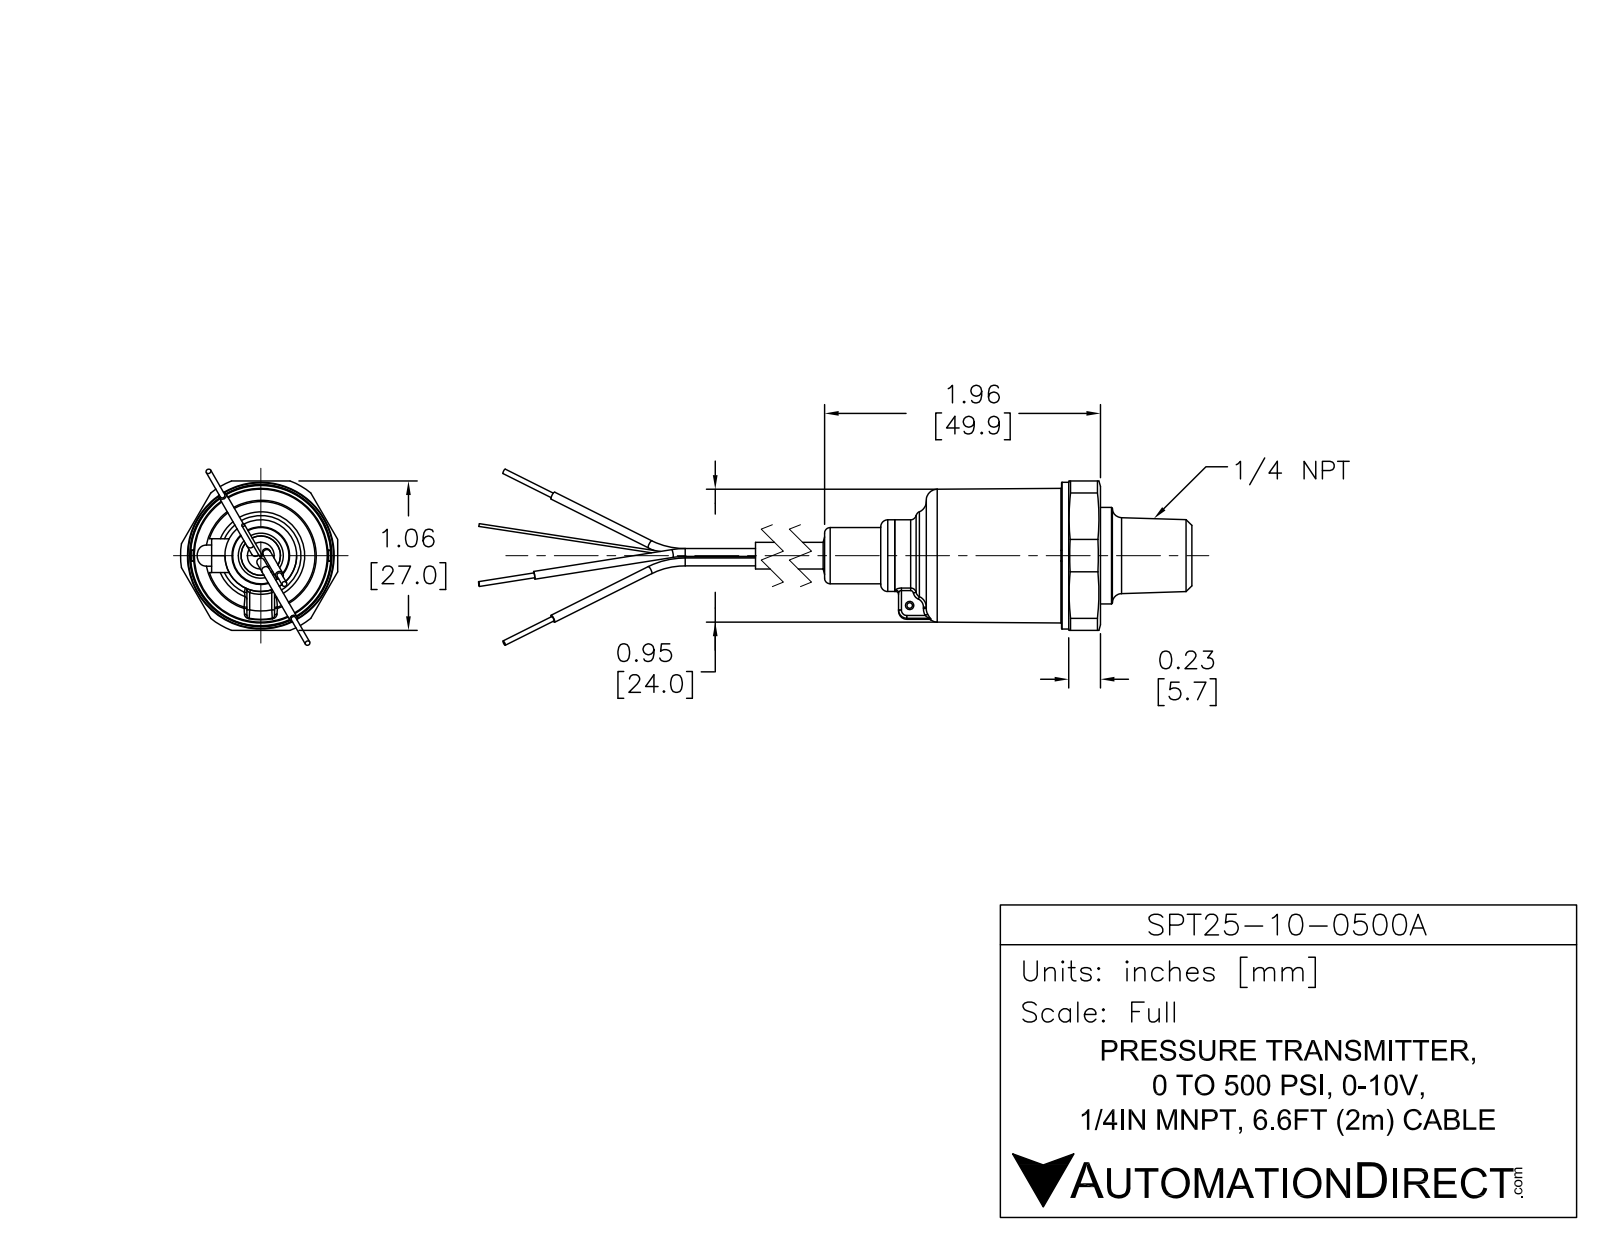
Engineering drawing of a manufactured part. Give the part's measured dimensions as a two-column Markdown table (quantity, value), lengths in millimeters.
| quantity | value |
| --- | --- |
| part name | SPT25-10-0500A |
| STEP written by | SolidWorks 2017 (AUTOMOTIVE_DESIGN) |
| units | millimeters |
| bodies | 7 solids, 116 faces (32 planar, 49 cylindrical, 35 other) |
| overall size | 153.3 × 29 × 27.09 |
| volume | 20 801 mm³ |
| surface area | 7 170 mm² |
| round holes (diameter × count) | 1 × 1, 3.3 × 1 |
| round bosses / shafts (diameter × count) | 1.4 × 6, 0.75 × 5, 26.75 × 1, 24 × 1, 17.5 × 1, 14 × 1, 13 × 1, 10 × 1 |
| partial cylindrical surfaces (radius × count) | 2 × 1, 14.5 × 1 |
| main face-to-face distances | 6.75, 24, 17.25, 42.75, 49.5, 66.75, 44, 1.25, 5.5, 22.75 |
